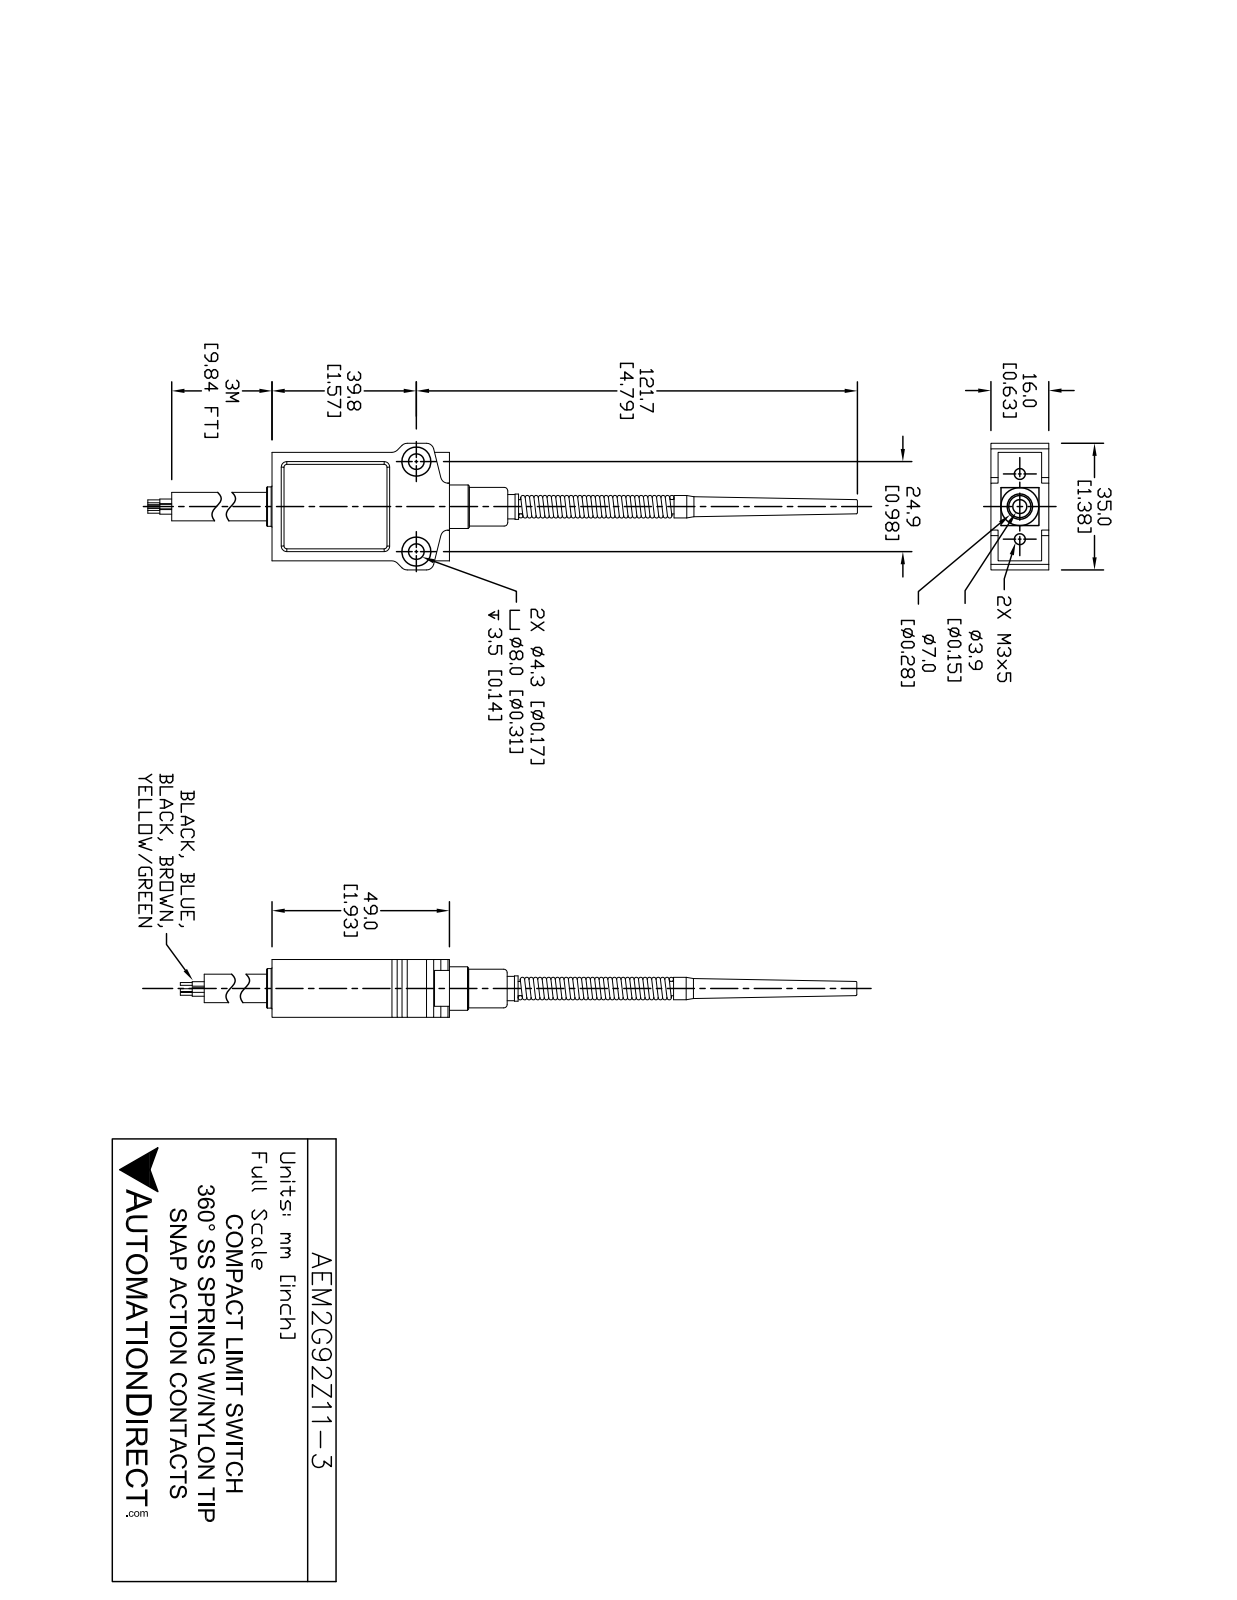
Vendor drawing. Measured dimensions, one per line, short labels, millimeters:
name: AEM2G92Z11-3_Default
written by: SolidWorks 2021 (CONFIG_CONTROL_DESIGN)
unit: mm
bodies: 1 solid, 117 faces (50 planar, 44 cylindrical, 23 other)
size: 177.8 × 35.1 × 16
volume: 25 740 mm³; area: 10 740 mm²
holes: 2× ⌀3, 2× ⌀4.5, 2× ⌀8.7
bosses: 5× ⌀1.3, 5× ⌀0.8, 1× ⌀11.9, 1× ⌀10.9, 1× ⌀10.7, 1× ⌀7.9, 1× ⌀7.1, 1× ⌀6.6
rounds: 8× R0.8, 8× R2
face distances: 0.8, 15.2, 14.5, 16, 30, 49, 2.5, 4.7, 11.3, 4
hole spacings: 19, 24.9
